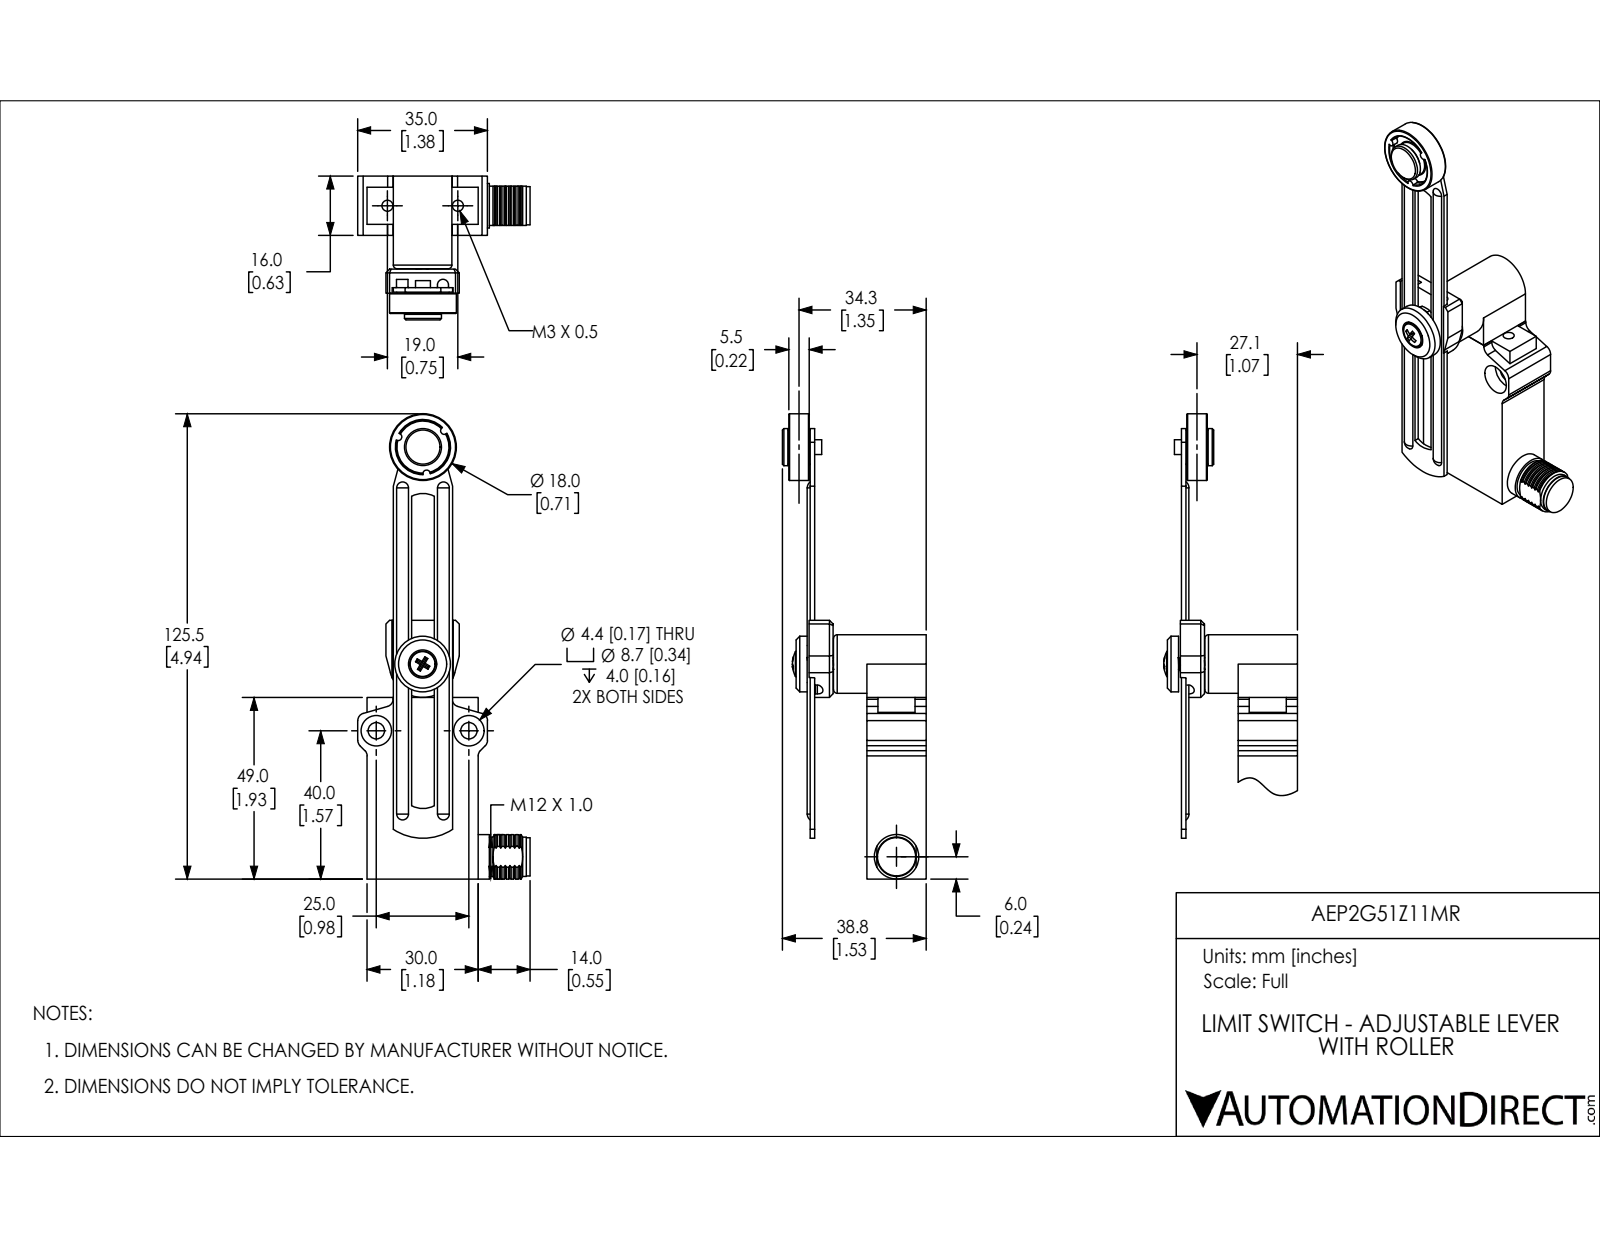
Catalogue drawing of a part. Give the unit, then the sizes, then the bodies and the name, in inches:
Units: inches
Overall size (bounding box): 4.941 × 1.831 × 1.528
Round holes (diameter × count): ⌀0.118 ×2, ⌀0.161 ×2, ⌀0.173 ×2, ⌀0.323 ×2, ⌀0.098 ×1, ⌀0.197 ×1, ⌀0.224 ×1, ⌀0.24 ×1, ⌀0.299 ×1
Round bosses / shafts (diameter × count): ⌀0.709 ×1, ⌀0.622 ×1, ⌀0.591 ×1, ⌀0.472 ×1, ⌀0.417 ×1, ⌀0.406 ×1, ⌀0.394 ×1, ⌀0.276 ×1
Partial cylindrical surfaces — rounded edges, fillets, slot ends (radius × count): R0.006 ×36, R0.079 ×10, R0.008 ×4, R0.047 ×4, R0.039 ×3, R0.256 ×3, R0.031 ×2, R0.059 ×1
Main face-to-face distances: 0.63, 0.047, 0.555, 1.185, 1.232, 0.602, 1.181, 0.28, 0.079, 1.929
Hole centre spacings: 0.863, 0.748, 0.984, 2.304, 3.052, 3.053
Volume: 2.061 in³ · Surface area: 24.68 in²
Bodies: 9 solids, 557 faces (198 planar, 253 cylindrical, 106 other)
Part name (STEP PRODUCT): AEP2G51Z11MR
STEP written by: SolidWorks 2018 (AUTOMOTIVE_DESIGN)
